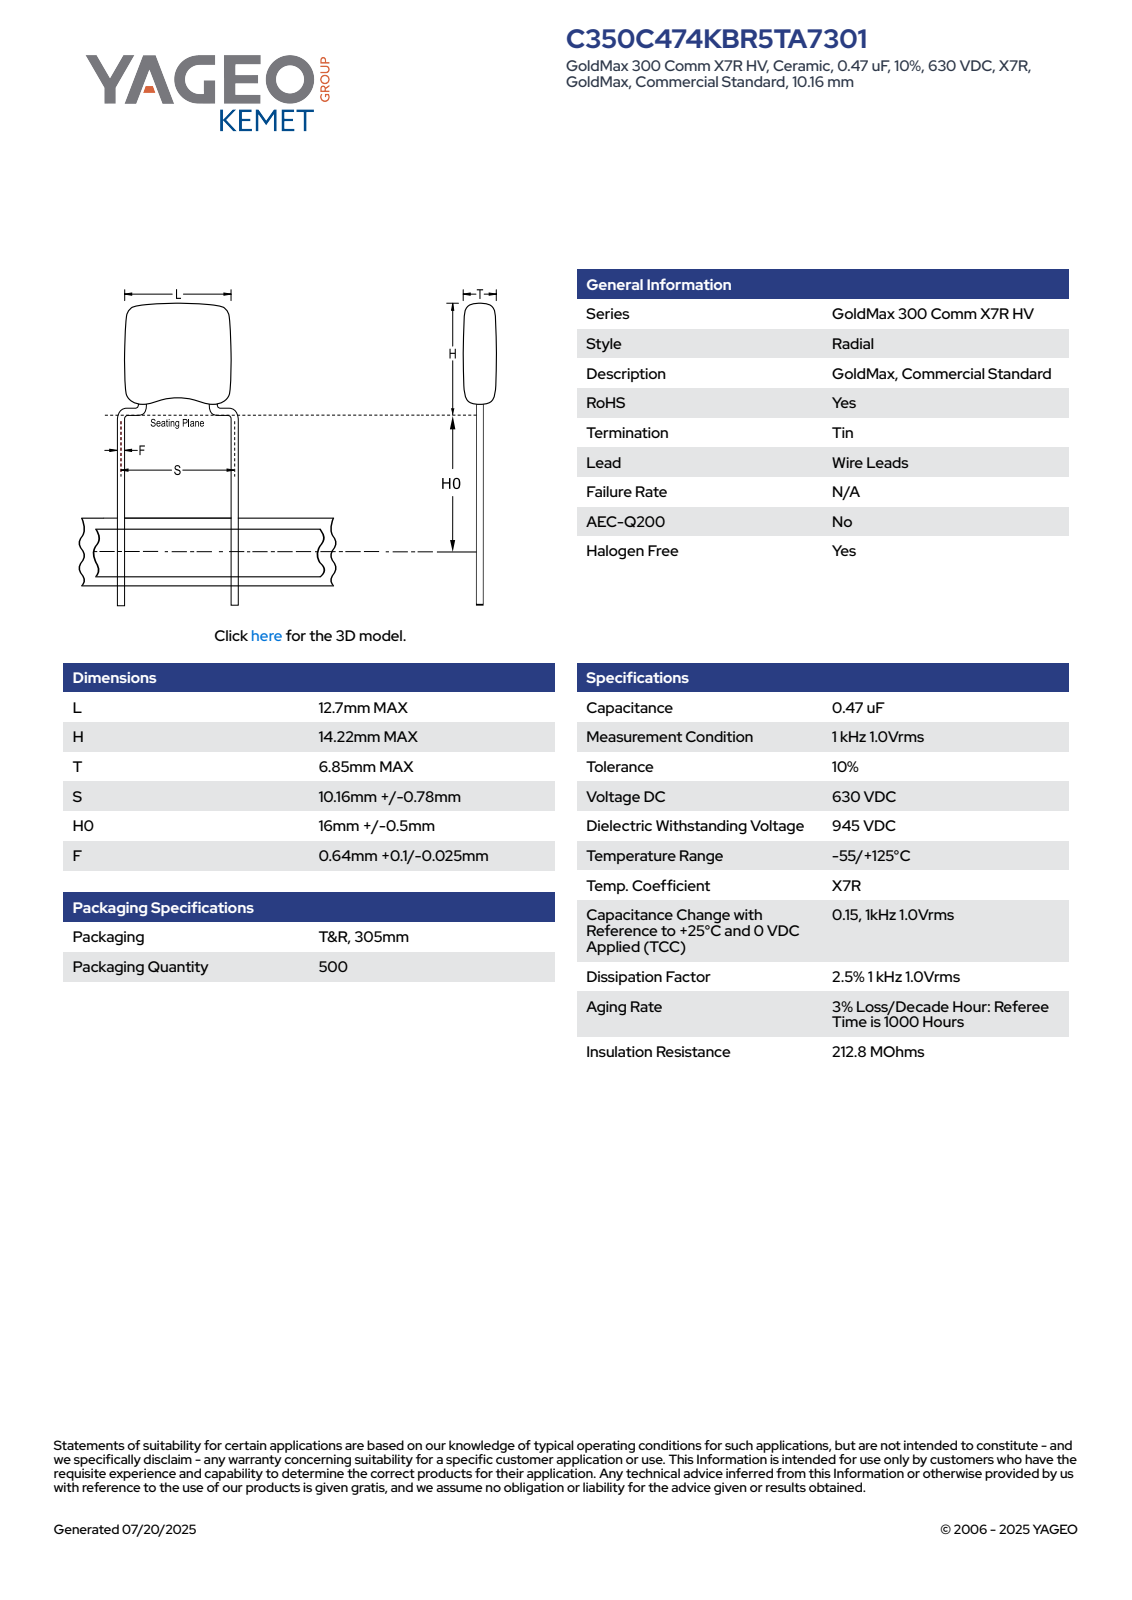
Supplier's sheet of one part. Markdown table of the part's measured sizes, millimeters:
| quantity | value |
| --- | --- |
| part name | CCR_SB_12.7X14.22_L12.7H14.22T6.85S10.16H016.5F0.64 |
| STEP written by | SolidWorks 2014 (AUTOMOTIVE_DESIGN) |
| units | millimeters |
| bodies | 4 solids, 97 faces (65 planar, 14 cylindrical, 18 other) |
| overall size | 30.72 × 12.7 × 6.86 |
| volume | 1 036 mm³ |
| surface area | 679 mm² |
| round bosses / shafts (diameter × count) | 0.64 × 2 |
| partial cylindrical surfaces (radius × count) | 1 × 10 |
| main face-to-face distances | 6.85, 12.03, 12.7, 1.08, 6.51, 5.52, 5.43, 6.6, 0.87, 2.22 |
